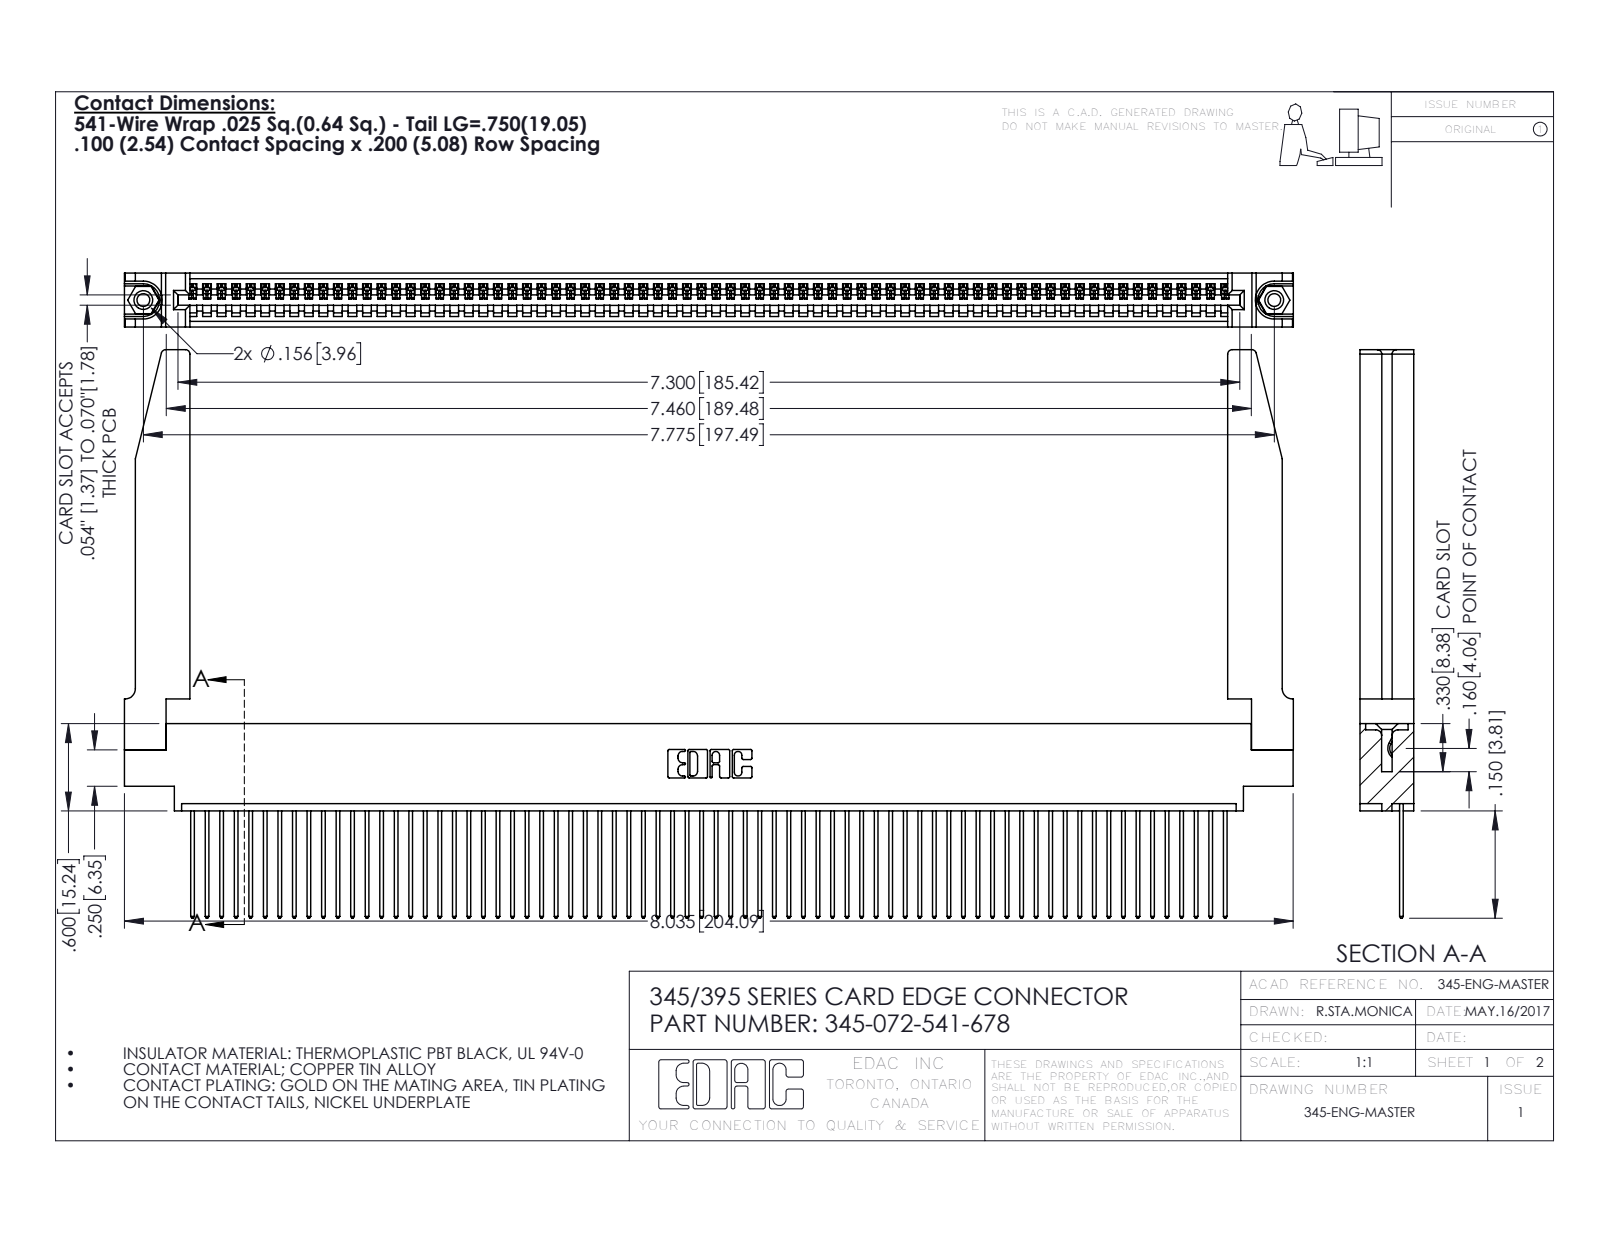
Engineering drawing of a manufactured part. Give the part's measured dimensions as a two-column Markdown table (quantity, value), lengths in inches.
| quantity | value |
| --- | --- |
| part name | 345-220-078_345-220-078; 345 Part_0.170 Offset - 0.156 Dia-TH; 345-072-541-678; 345-250-001_345-250-001-102 (+1 more) |
| STEP written by | SolidWorks 2016 (CONFIG_CONTROL_DESIGN) |
| units | inches |
| bodies | 77 solids, 4540 faces (3106 planar, 1382 cylindrical, 52 other) |
| overall size | 8.036 × 3.907 × 0.37 |
| volume | 1.68 in³ |
| surface area | 54.3 in² |
| round holes (diameter × count) | 0.089 × 2, 0.125 × 2, 0.156 × 2, 0.064 × 1 |
| round bosses / shafts (diameter × count) | 0.155 × 2 |
| partial cylindrical surfaces (radius × count) | 0.006 × 144, 0.01 × 144, 0.01 × 22, 0.03 × 8, 0.007 × 6, 0.031 × 6, 0.026 × 3, 0.031 × 2 |
| main face-to-face distances | 0.072, 0.298, 0.37, 0.098, 0.272, 0.025, 0.2, 0.225, 0.149, 0.175 |
| hole center spacings | 0.27, 7.539, 7.775 |
